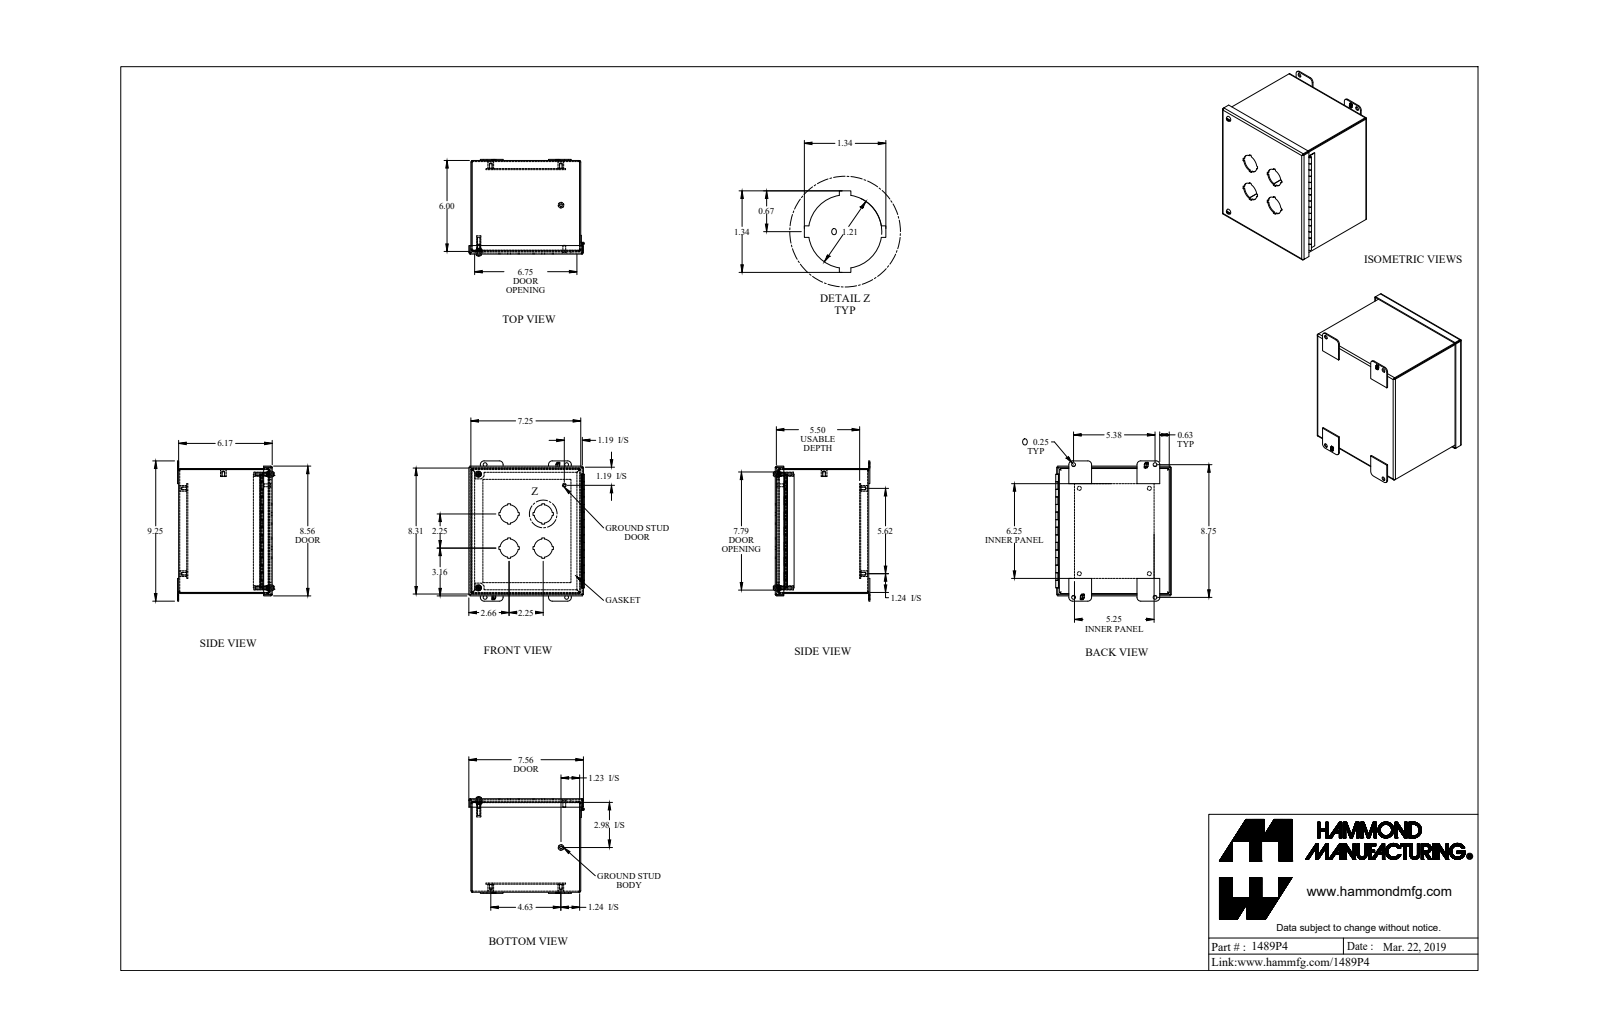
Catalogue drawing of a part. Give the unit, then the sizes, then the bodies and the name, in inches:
Units: inches
Overall size (bounding box): 9.25 × 7.623 × 6.371
Round holes (diameter × count): ⌀0.25 ×6, ⌀0.156 ×5, ⌀0.265 ×4, ⌀1.21 ×4, ⌀0.159 ×2, ⌀0.406 ×2
Round bosses / shafts (diameter × count): ⌀0.375 ×5, ⌀0.39 ×2, ⌀0.275 ×2, ⌀0.19 ×2, ⌀0.148 ×2, ⌀0.25 ×1, ⌀0.188 ×1, ⌀0.174 ×1
Partial cylindrical surfaces — rounded edges, fillets, slot ends (radius × count): R0.036 ×12, R0.108 ×12, R0.25 ×8, R0.16 ×2, R0.171 ×2
Main face-to-face distances: 0.072, 6.1, 7.178, 0.072, 8.178, 5.568, 0.532, 6.172, 6.028, 7.25
Hole centre spacings: 4.625, 5.239, 7.5, 2.25, 5.536, 5.624, 7.282, 1.228
Volume: 30.66 in³ · Surface area: 817.9 in²
Bodies: 21 solids, 726 faces (484 planar, 176 cylindrical, 66 other)
Part name (STEP PRODUCT): 1489P4_Default
STEP written by: SolidWorks 2019 (CONFIG_CONTROL_DESIGN)
